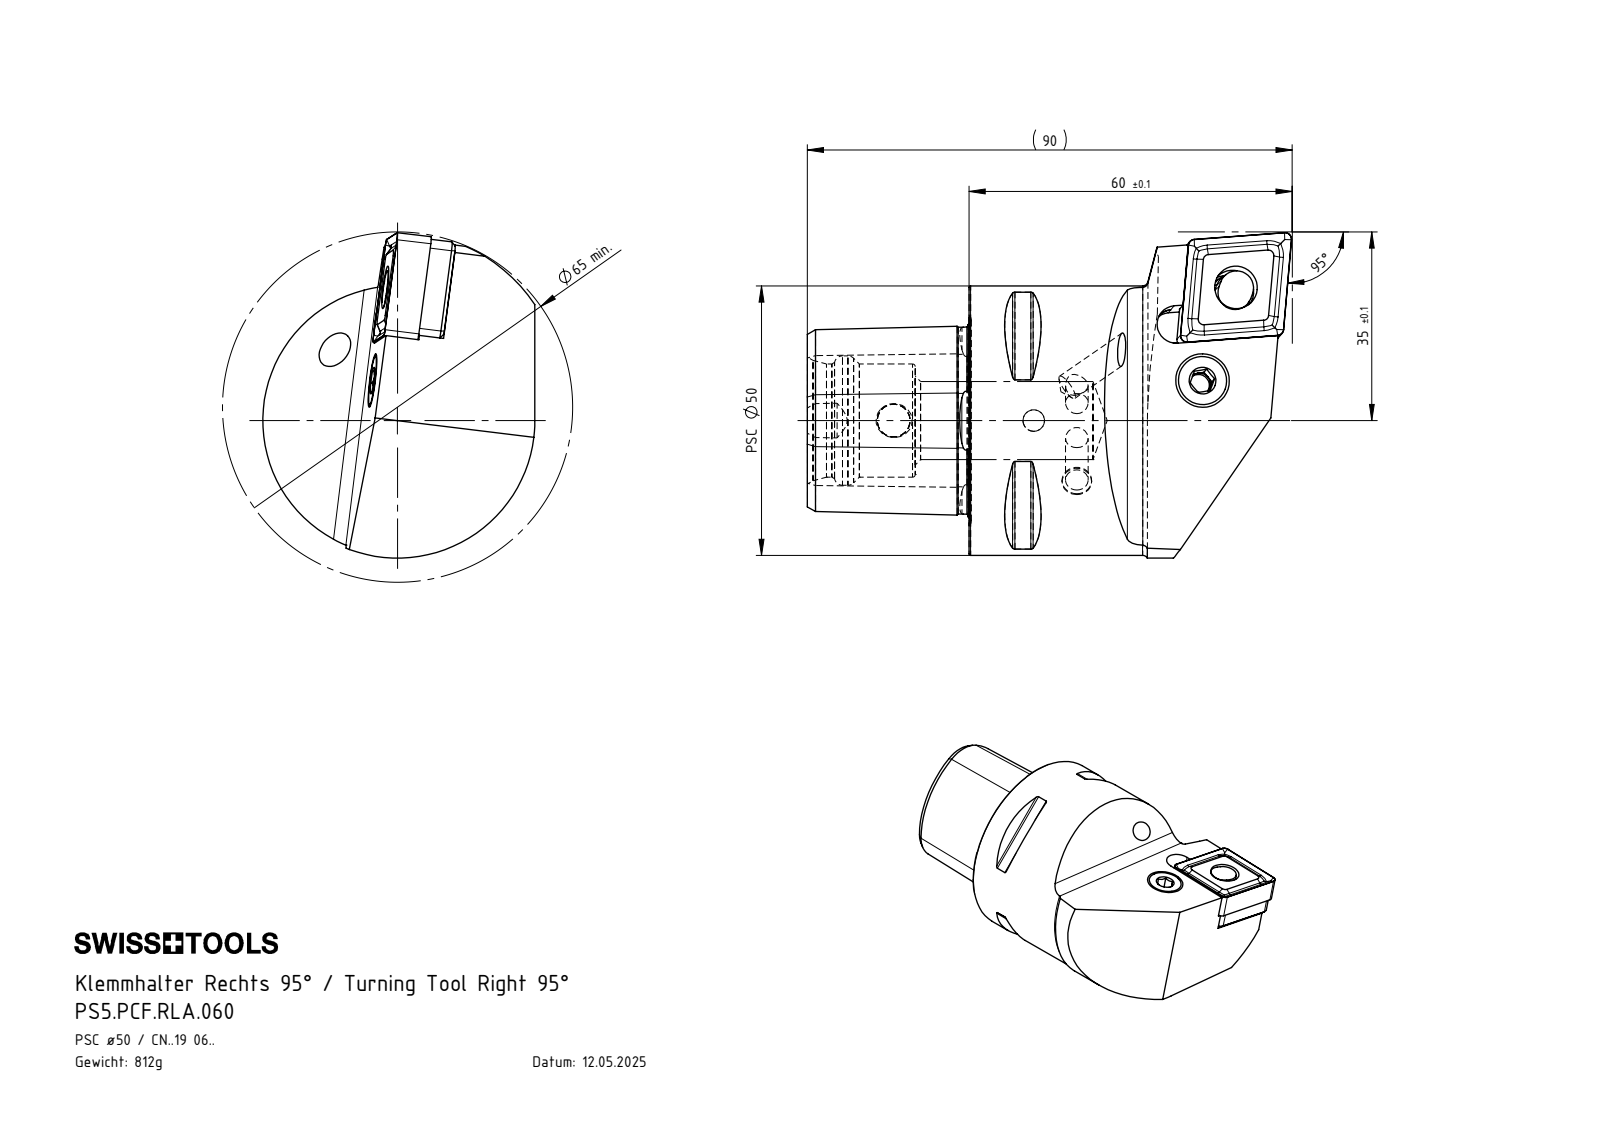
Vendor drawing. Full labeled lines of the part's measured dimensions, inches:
Part name (STEP PRODUCT): PS5-PCF.RLA.060_A_Fertigbearbeitung; PS5.PCF.RLA.060; ISO 4026 - M5 x 5; WCF-ER3.101.000_A (+4 more)
STEP written by: SolidWorks 2022 (AUTOMOTIVE_DESIGN)
Units: inches
Bodies: 7 solids, 341 faces (109 planar, 81 cylindrical, 151 other)
Overall size (bounding box): 3.538 × 2.378 × 1.988
Volume: 6.209 in³ · Surface area: 38.93 in²
Round holes (diameter × count): ⌀0.157 ×2, ⌀0.165 ×1, ⌀0.197 ×1, ⌀0.217 ×1, ⌀0.24 ×1, ⌀0.313 ×1, ⌀0.354 ×1, ⌀0.378 ×1, ⌀0.402 ×1, ⌀0.571 ×1, ⌀0.827 ×1, ⌀0.945 ×1
Round bosses / shafts (diameter × count): ⌀1.969 ×1, ⌀0.394 ×1, ⌀0.39 ×1, ⌀0.339 ×1, ⌀0.197 ×1, ⌀0.175 ×1
Partial cylindrical surfaces — rounded edges, fillets, slot ends (radius × count): R0.02 ×8, R0.047 ×4, R0.059 ×4, R0.157 ×4, R0.122 ×1, R0.13 ×1, R0.138 ×1, R0.144 ×1
Main face-to-face distances: 1.181, 0.234, 0.031, 0.75, 0.719, 0.189, 0.422, 0.188, 0.234, 0.721
Hole centre spacings: 0.013, 0.729, 0.729, 0.74, 0.74, 1.024
